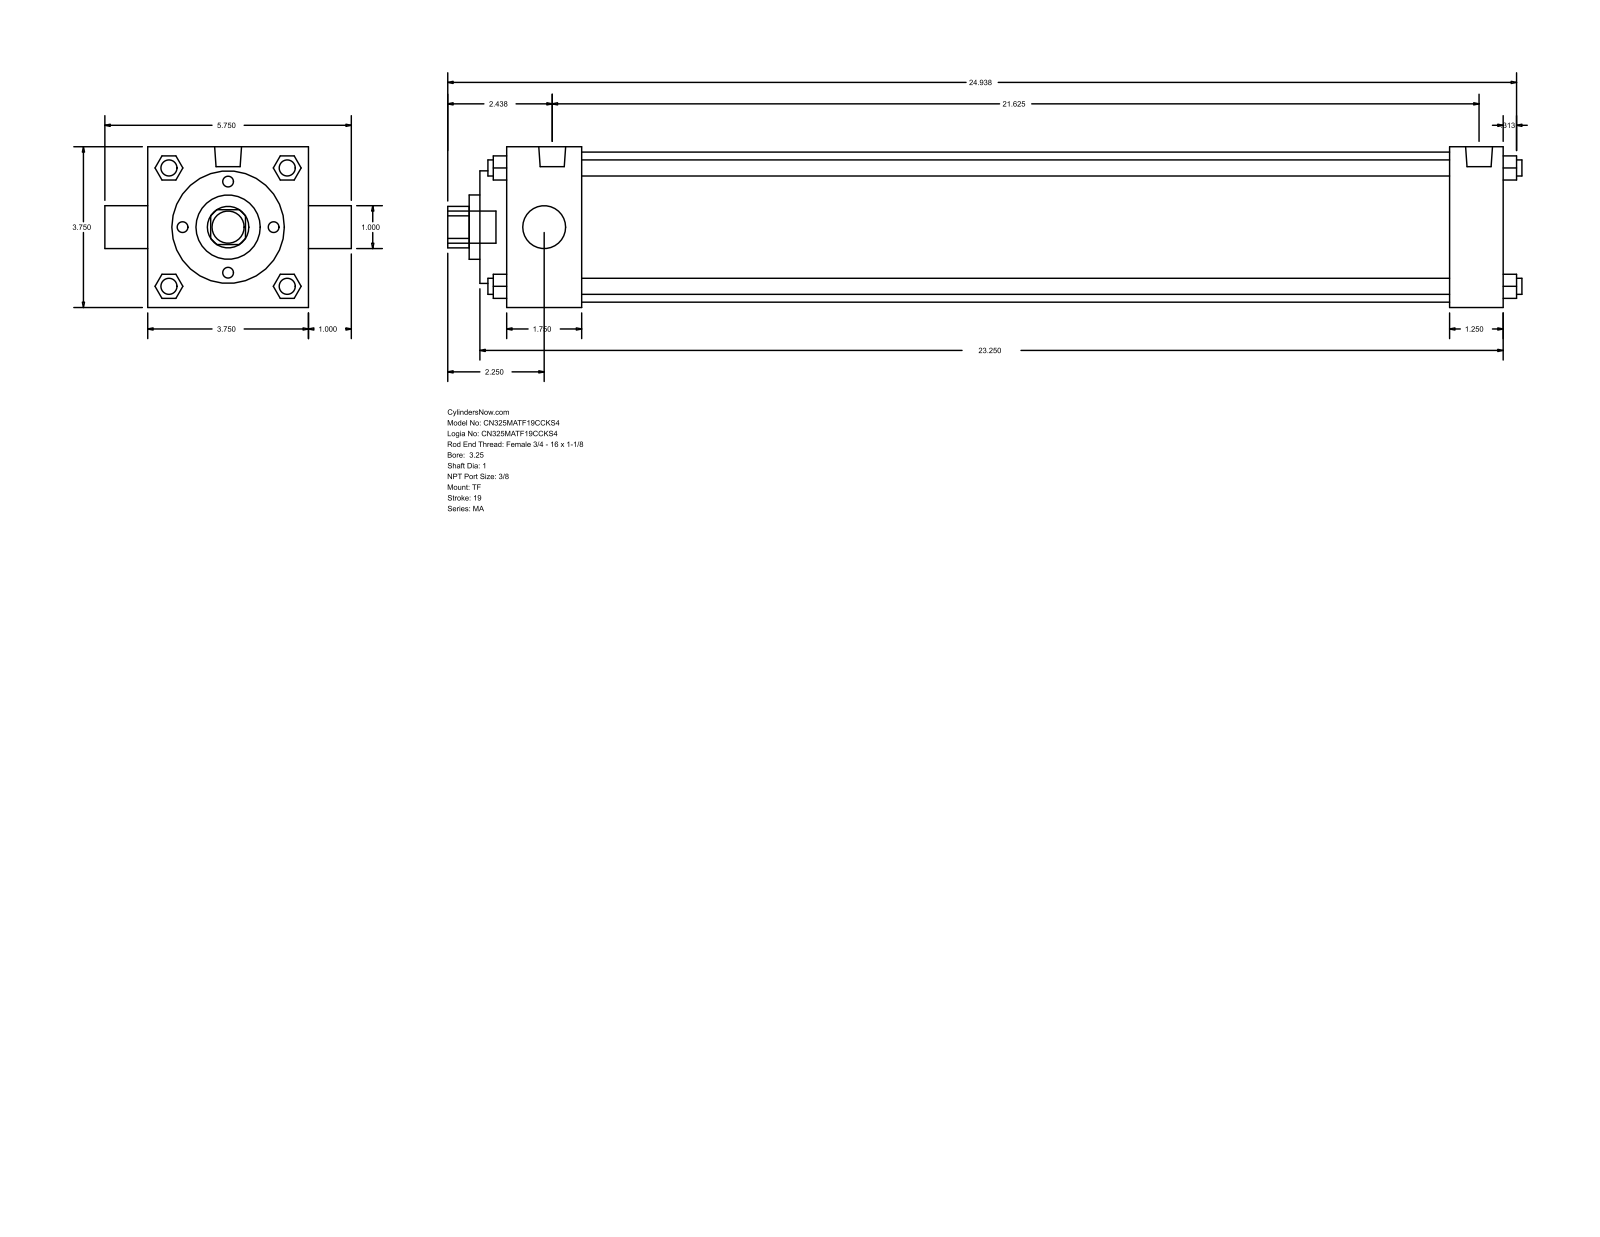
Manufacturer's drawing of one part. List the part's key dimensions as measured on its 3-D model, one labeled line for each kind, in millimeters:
Part name (STEP PRODUCT): MA_TF__0325_1
STEP written by: GSSL Pune (CONFIG_CONTROL_DESIGN)
Units: millimetres
Bodies: 0 solids, 122 faces (93 planar, 29 cylindrical, 0 other)
Overall size (bounding box): 636.59 × 146.05 × 95.25
Round holes (diameter × count): ⌀25.4 ×2, ⌀38.1 ×1, ⌀66.67 ×1, ⌀88.9 ×1
Round bosses / shafts (diameter × count): ⌀9.53 ×4, ⌀11.11 ×3, ⌀15.93 ×2, ⌀19.05 ×1
Partial cylindrical surfaces — rounded edges, fillets, slot ends (radius × count): R12.29 ×1
Main face-to-face distances: 95.24, 590.56, 15.87, 44.46, 558.81, 514.35, 546.1, 31.75, 60.33, 574.68
